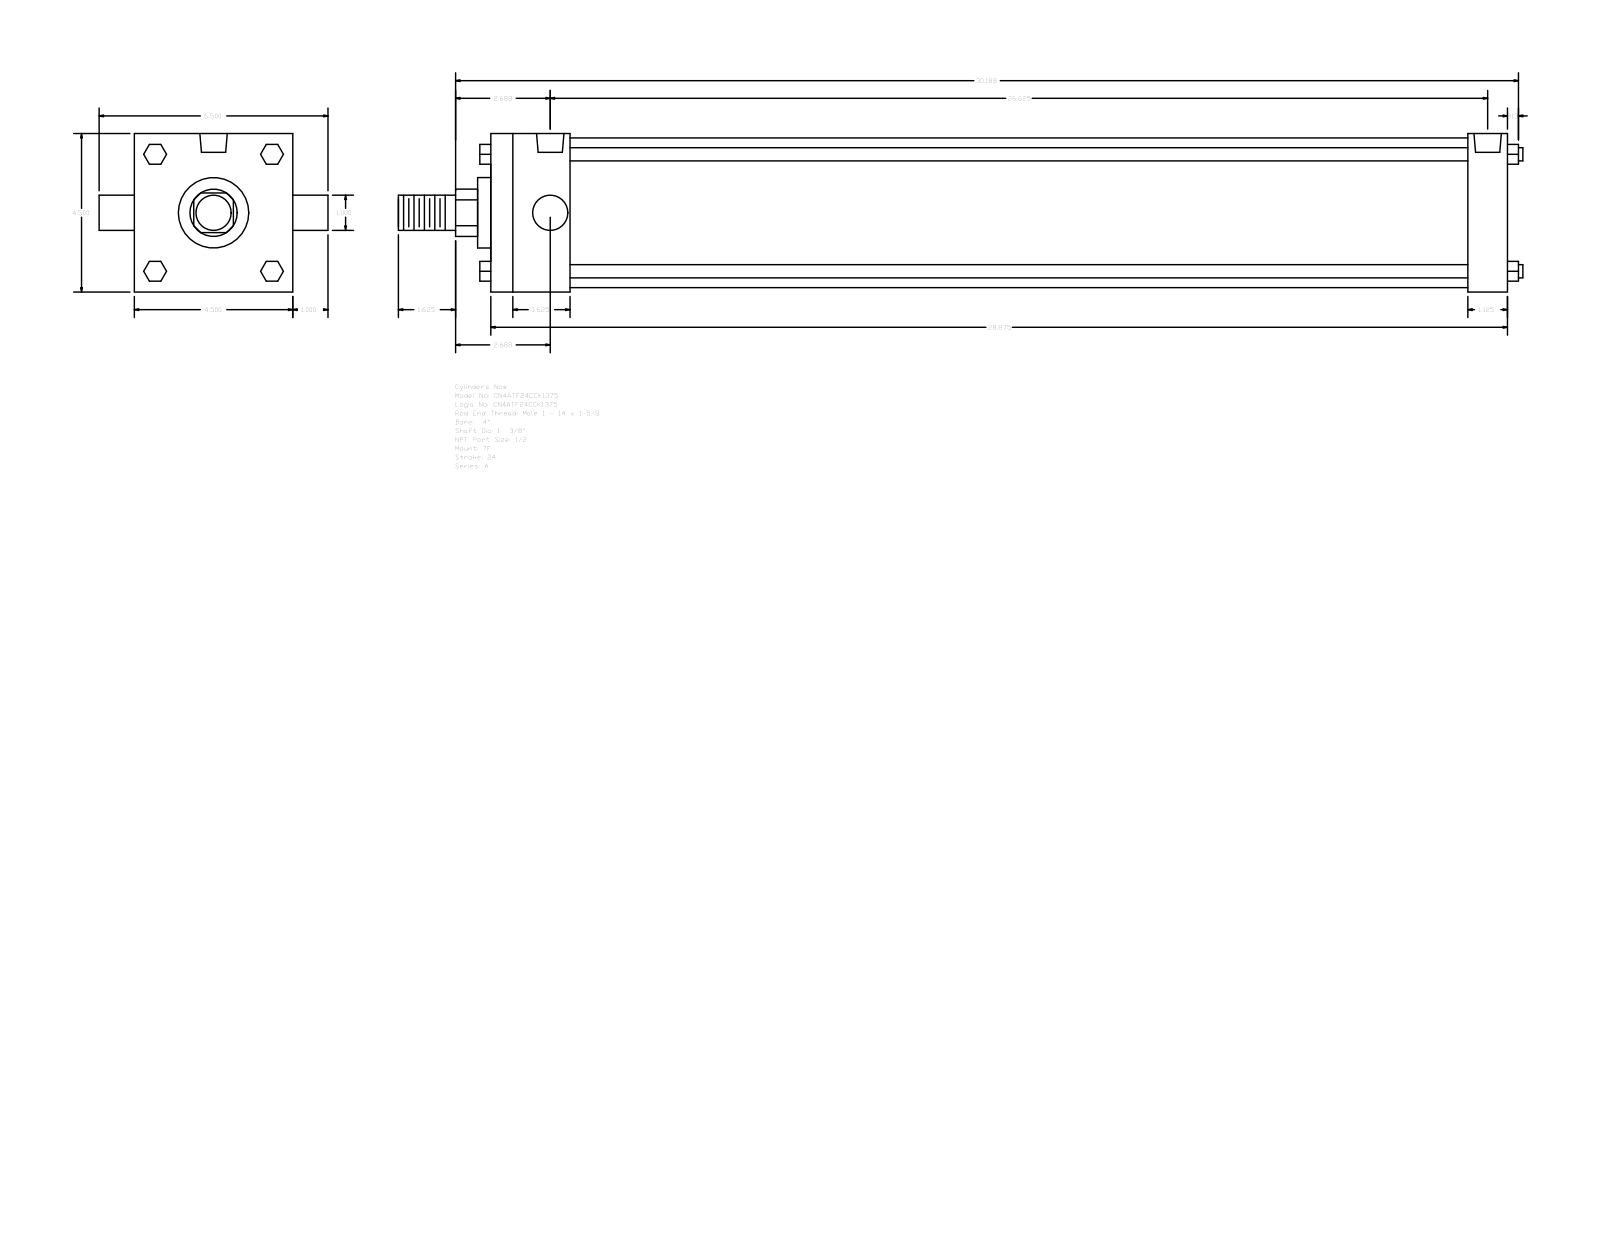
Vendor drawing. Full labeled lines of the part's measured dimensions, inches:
Part name (STEP PRODUCT): A_TF__0400_1.375
STEP written by: GSSL Pune (CONFIG_CONTROL_DESIGN)
Units: inches
Bodies: 0 solids, 120 faces (92 planar, 28 cylindrical, 0 other)
Overall size (bounding box): 31.937 × 6.5 × 4.5
Round holes (diameter × count): ⌀0.344 ×3, ⌀0.778 ×2
Round bosses / shafts (diameter × count): ⌀0.375 ×4, ⌀1 ×2, ⌀4.25 ×1, ⌀2 ×1, ⌀1.375 ×1
Partial cylindrical surfaces — rounded edges, fillets, slot ends (radius × count): R0.672 ×1
Main face-to-face distances: 4.5, 28.875, 2.25, 1.125, 27.75, 25.5, 26.625, 2.625, 0.563, 1
Hole centre spacings: 0.125, 26.5, 26.375, 26.625
